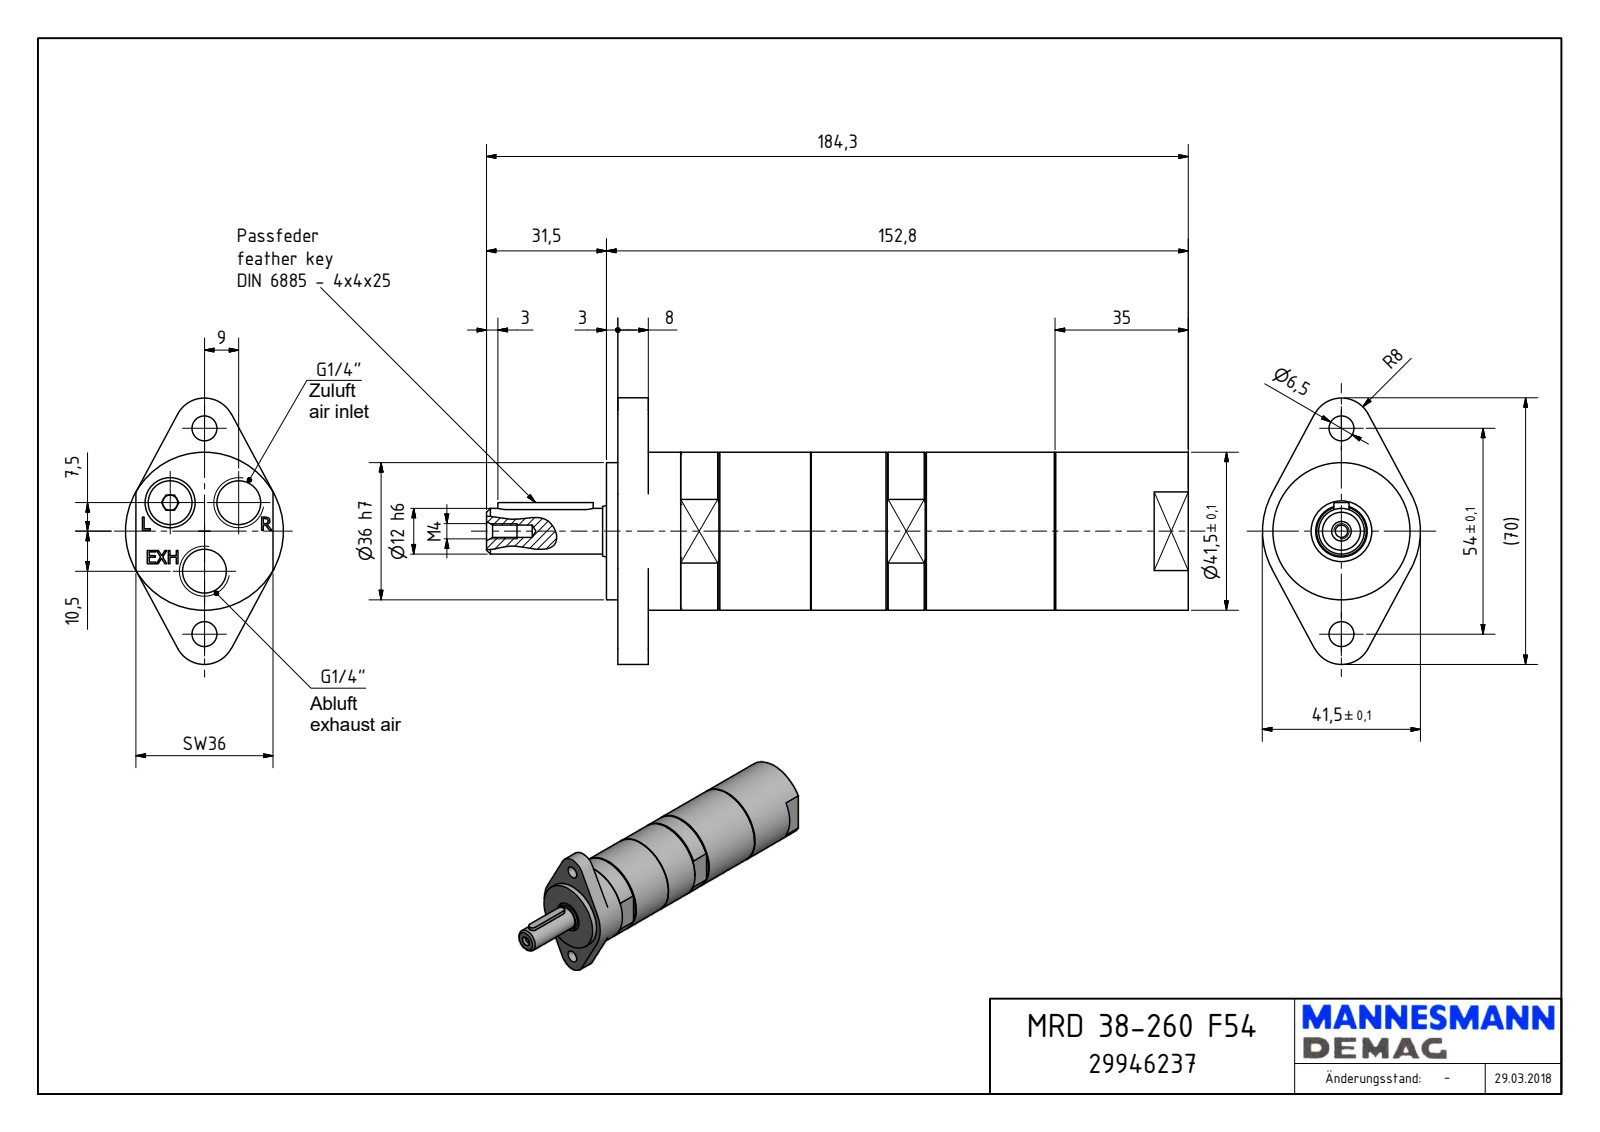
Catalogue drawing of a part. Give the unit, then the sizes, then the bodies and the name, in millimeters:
Units: millimetres
Overall size (bounding box): 184.2 × 70 × 41.5
Round holes (diameter × count): ⌀11.45 ×3, ⌀6.5 ×2, ⌀3.24 ×1, ⌀4 ×1, ⌀16 ×1, ⌀37.5 ×1, ⌀37.99 ×1
Round bosses / shafts (diameter × count): ⌀41.5 ×1, ⌀37.45 ×1, ⌀36 ×1, ⌀14.95 ×1, ⌀12 ×1
Partial cylindrical surfaces — rounded edges, fillets, slot ends (radius × count): R5.71 ×78, R2 ×2, R8 ×2, R16.39 ×1, R16.6 ×1
Main face-to-face distances: 149.7, 3, 152.7, 11, 8, 141.7, 1, 42.5, 41.48, 37
Hole centre spacings: 11.72, 20.12, 21.48, 27, 35.65, 10.5, 16.5, 18
Volume: 209 215 mm³ · Surface area: 34 034 mm²
Bodies: 1 solid, 411 faces (190 planar, 188 cylindrical, 33 other)
Part name (STEP PRODUCT): MRD 38-260 F70_29946237
STEP written by: Autodesk Inventor 2018 (AUTOMOTIVE_DESIGN)
